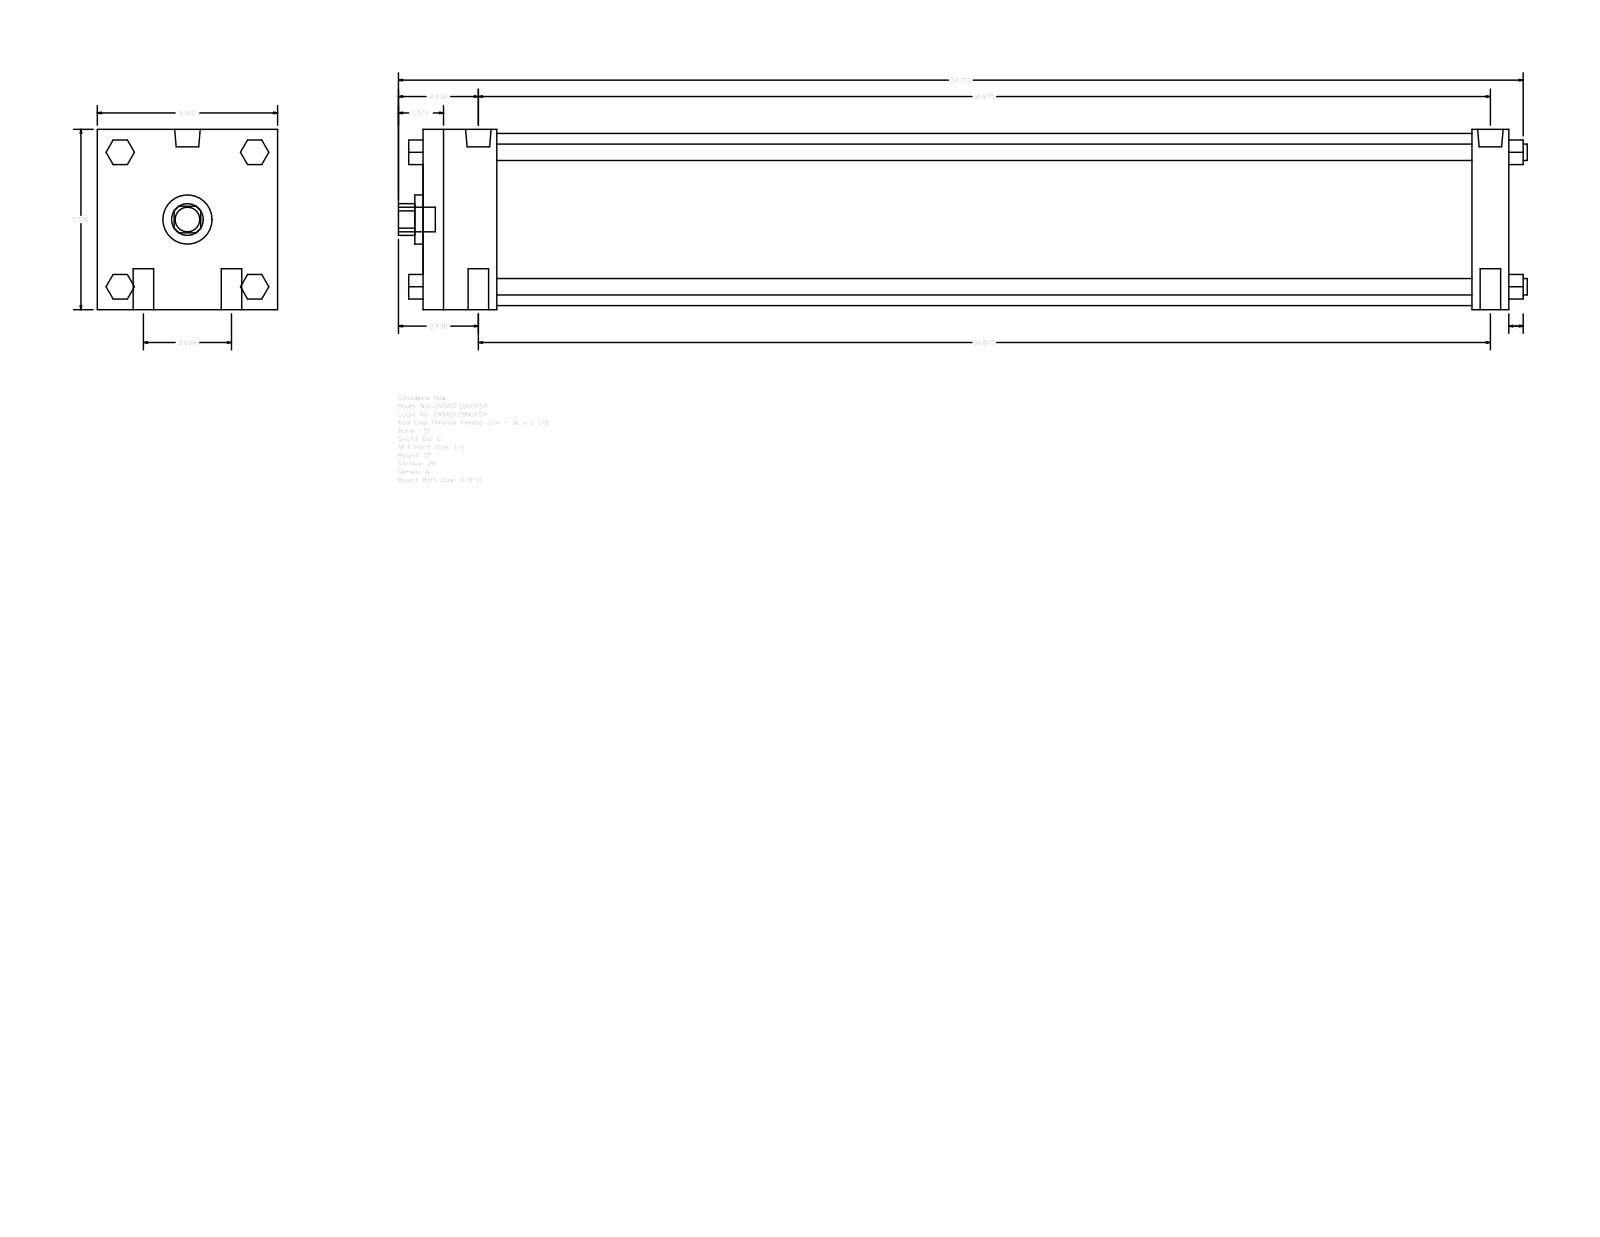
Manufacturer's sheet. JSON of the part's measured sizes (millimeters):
{"part_name": "A_SF__0500_1", "step_written_by": "GSSL Pune (CONFIG_CONTROL_DESIGN)", "units": "millimeters", "bodies": {"solids": 0, "faces": 124, "planar": 94, "cylindrical": 30, "other": 0}, "overall_size": [874.71, 139.7, 139.7], "round_holes": [[25.4, 1], [38.1, 1], [133.35, 1]], "round_bosses_or_shafts": [[15.88, 4], [12.7, 4], [19.77, 2], [8.73, 2], [19.05, 1]], "partial_cylinders_radius": [[12.29, 1]], "face_to_face_distances": [139.7, 841.37, 28.57, 57.15, 812.8, 755.65, 784.22, 19.05, 52.07, 90.18]}
